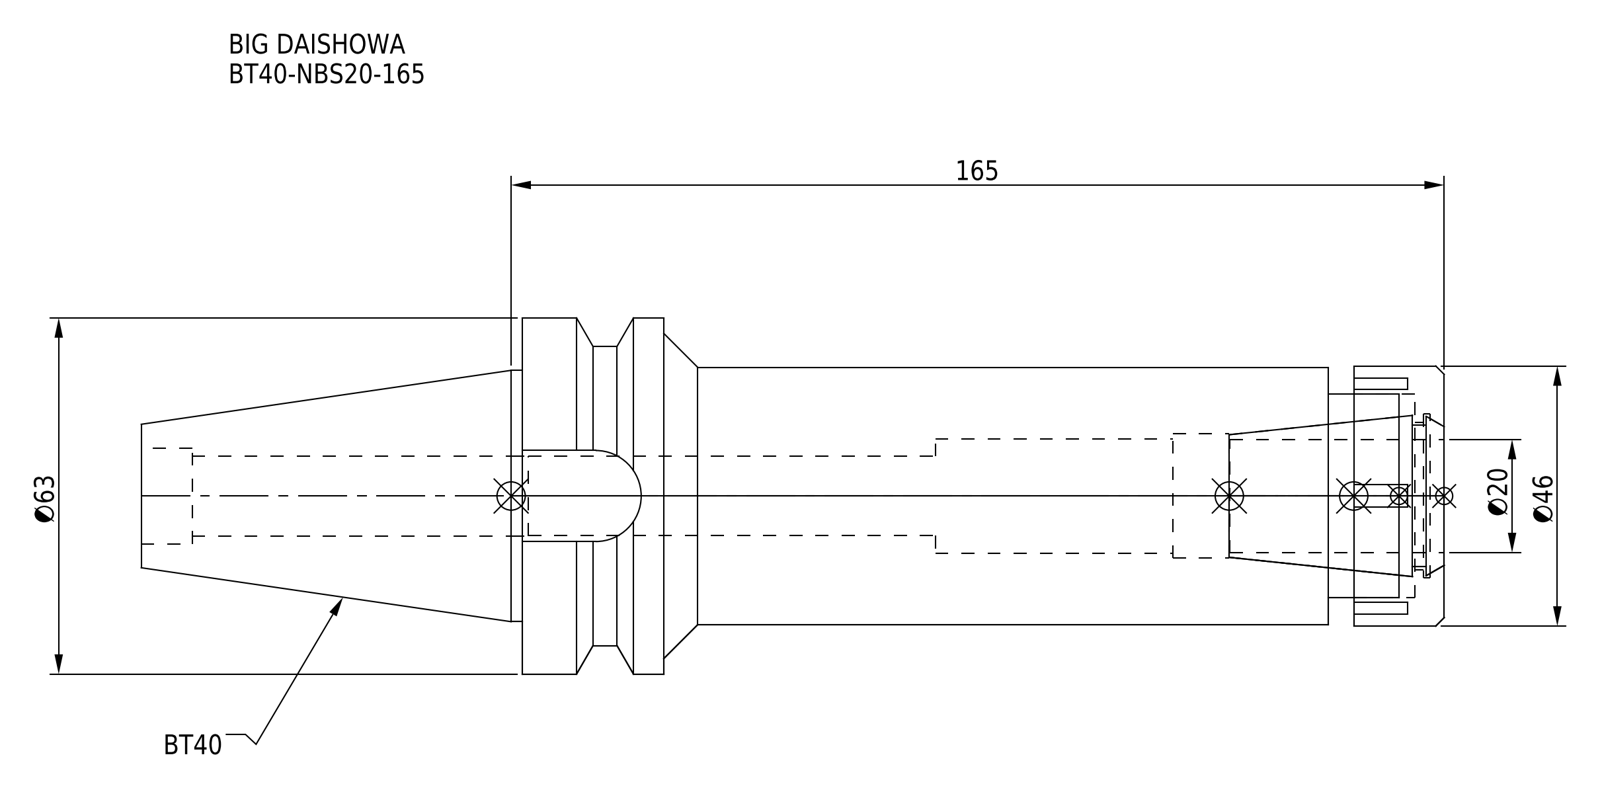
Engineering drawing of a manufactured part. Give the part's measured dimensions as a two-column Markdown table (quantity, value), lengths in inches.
| quantity | value |
| --- | --- |
| part name | BT40-NBS20-165_1.stp; BT40-NBS20-165-FreeParts; BT40-NBS20-165.stp; NBN20_1.stp (+3 more) |
| STEP written by | SolidWorks 2019 (CONFIG_CONTROL_DESIGN) |
| units | inches |
| bodies | 2 solids, 93 faces (45 planar, 34 cylindrical, 14 other) |
| overall size | 9.071 × 2.48 × 2.48 |
| volume | 18.2 in³ |
| surface area | 84.77 in² |
| round holes (diameter × count) | 0.551 × 1, 0.559 × 1, 0.669 × 1, 0.799 × 1, 0.866 × 1, 1.024 × 1, 1.142 × 1, 1.417 × 1 |
| round bosses / shafts (diameter × count) | 2.48 × 1, 2.087 × 1, 1.811 × 1, 1.791 × 1, 1.75 × 1 |
| partial cylindrical surfaces (radius × count) | 0.317 × 1 |
| main face-to-face distances | 6.417, 0.315, 0.807, 5.61, 0.63, 0.177, 5.787, 5.433, 4.803, 4.626 |
